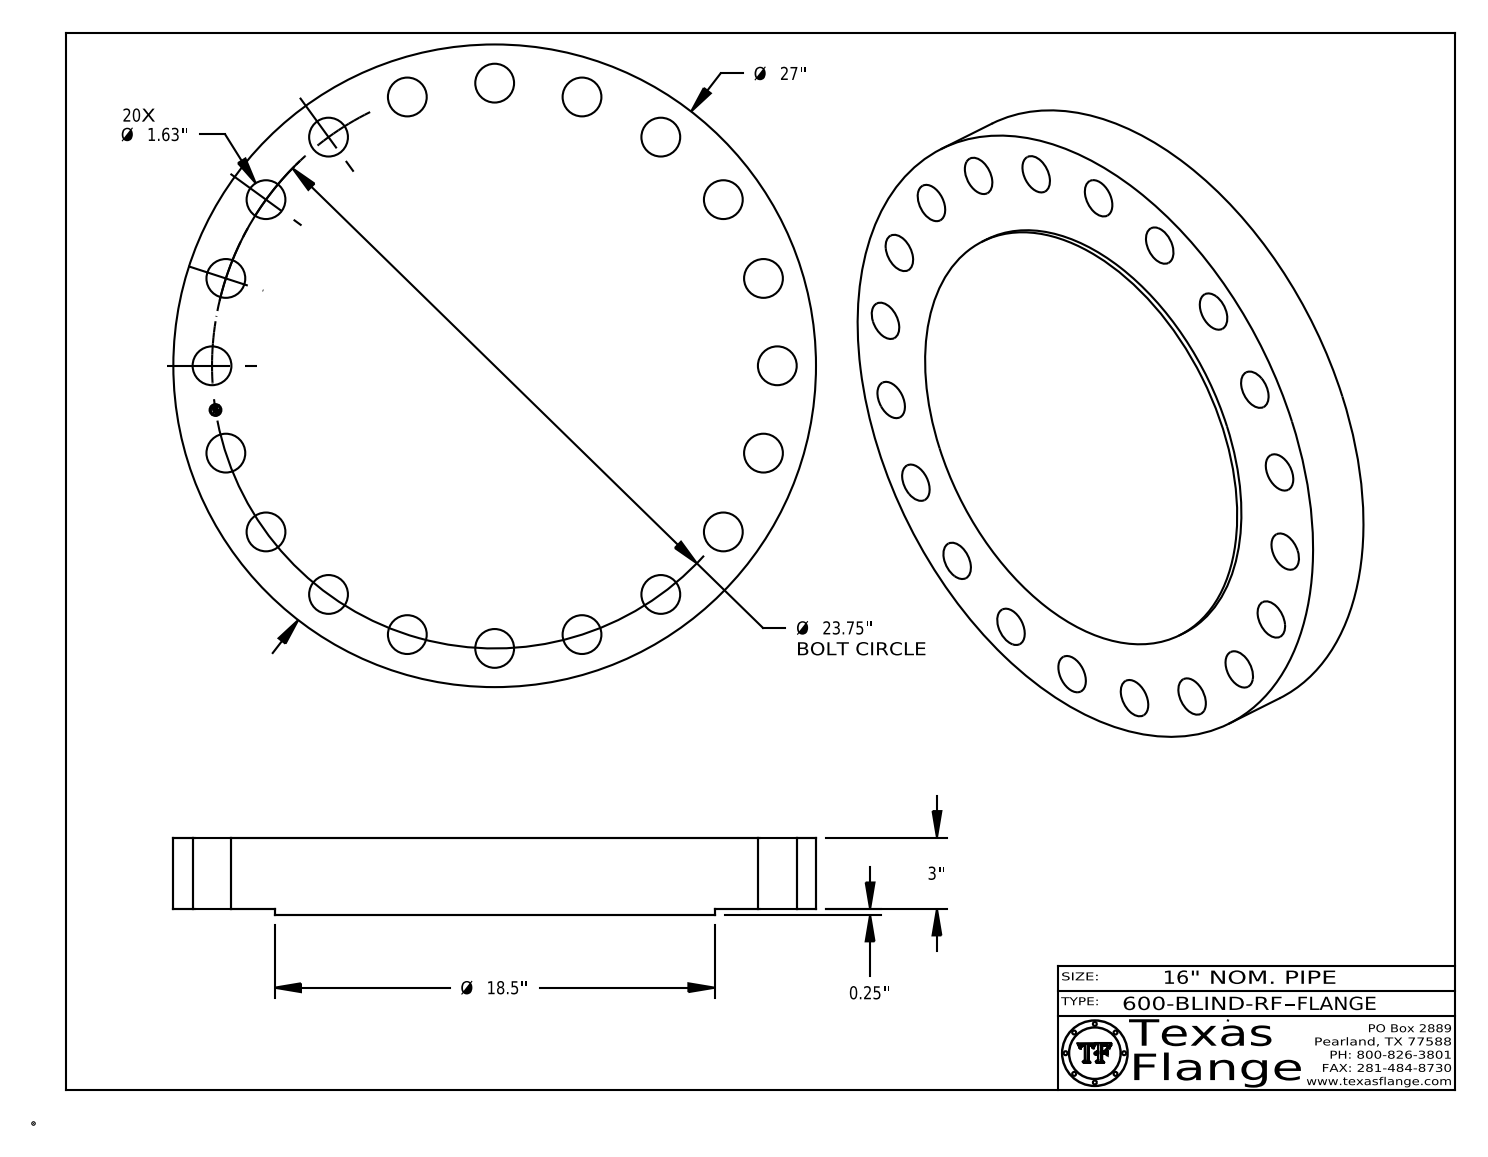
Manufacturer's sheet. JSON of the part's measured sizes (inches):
{"part_name": "600-BLIND-RF", "step_written_by": "CATIA V5 STEP AP214 (AUTOMOTIVE_DESIGN)", "units": "inches", "bodies": {"solids": 1, "faces": 432, "planar": 368, "cylindrical": 64, "other": 0}, "overall_size": [27, 27, 3.25], "volume_in3": 1660, "surface_area_in2": 1638, "round_holes": [[1.63, 20], [0.495, 1]], "round_bosses_or_shafts": [[0.03, 8], [27, 1], [18.5, 1], [0.39, 1]], "face_to_face_distances": [3.25, 0.25, 3, 3.235, 2.985, 0.015, 0.148, 0.144, 0.027, 0.096], "hole_center_spacings": [16.794, 19.214, 22.587, 23.457, 7.339, 10.782, 3.715, 13.96]}
